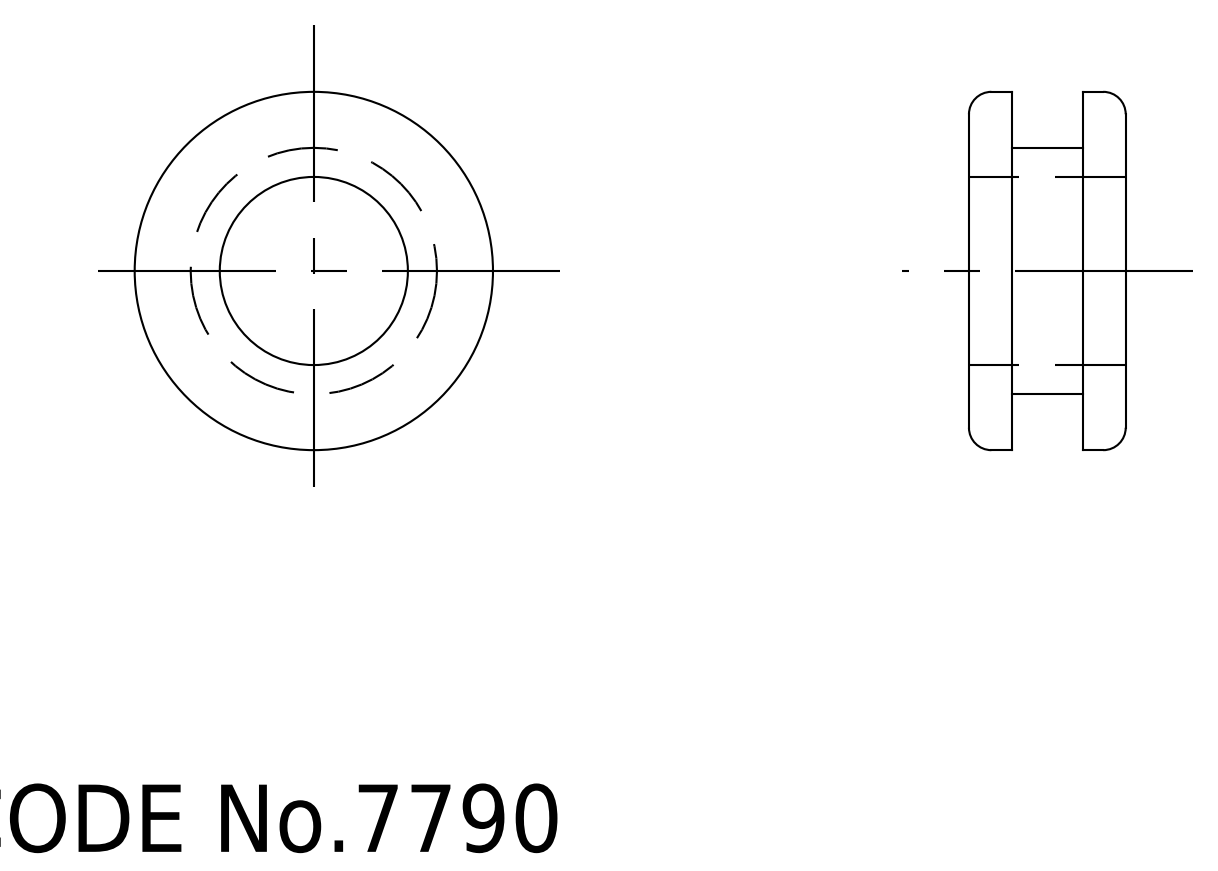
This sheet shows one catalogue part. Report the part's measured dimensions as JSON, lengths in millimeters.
{"part_name": "TM_346_5", "step_written_by": "SolidWorks 2015 (AUTOMOTIVE_DESIGN)", "units": "millimeters", "bodies": {"solids": 1, "faces": 16, "planar": 4, "cylindrical": 8, "other": 4}, "overall_size": [16, 16, 7], "volume_mm3": 659, "surface_area_mm2": 946, "round_holes": [[8.4, 1]], "round_bosses_or_shafts": [[16, 1], [11, 1]], "face_to_face_distances": [1.9, 5.1, 3.2, 7]}
